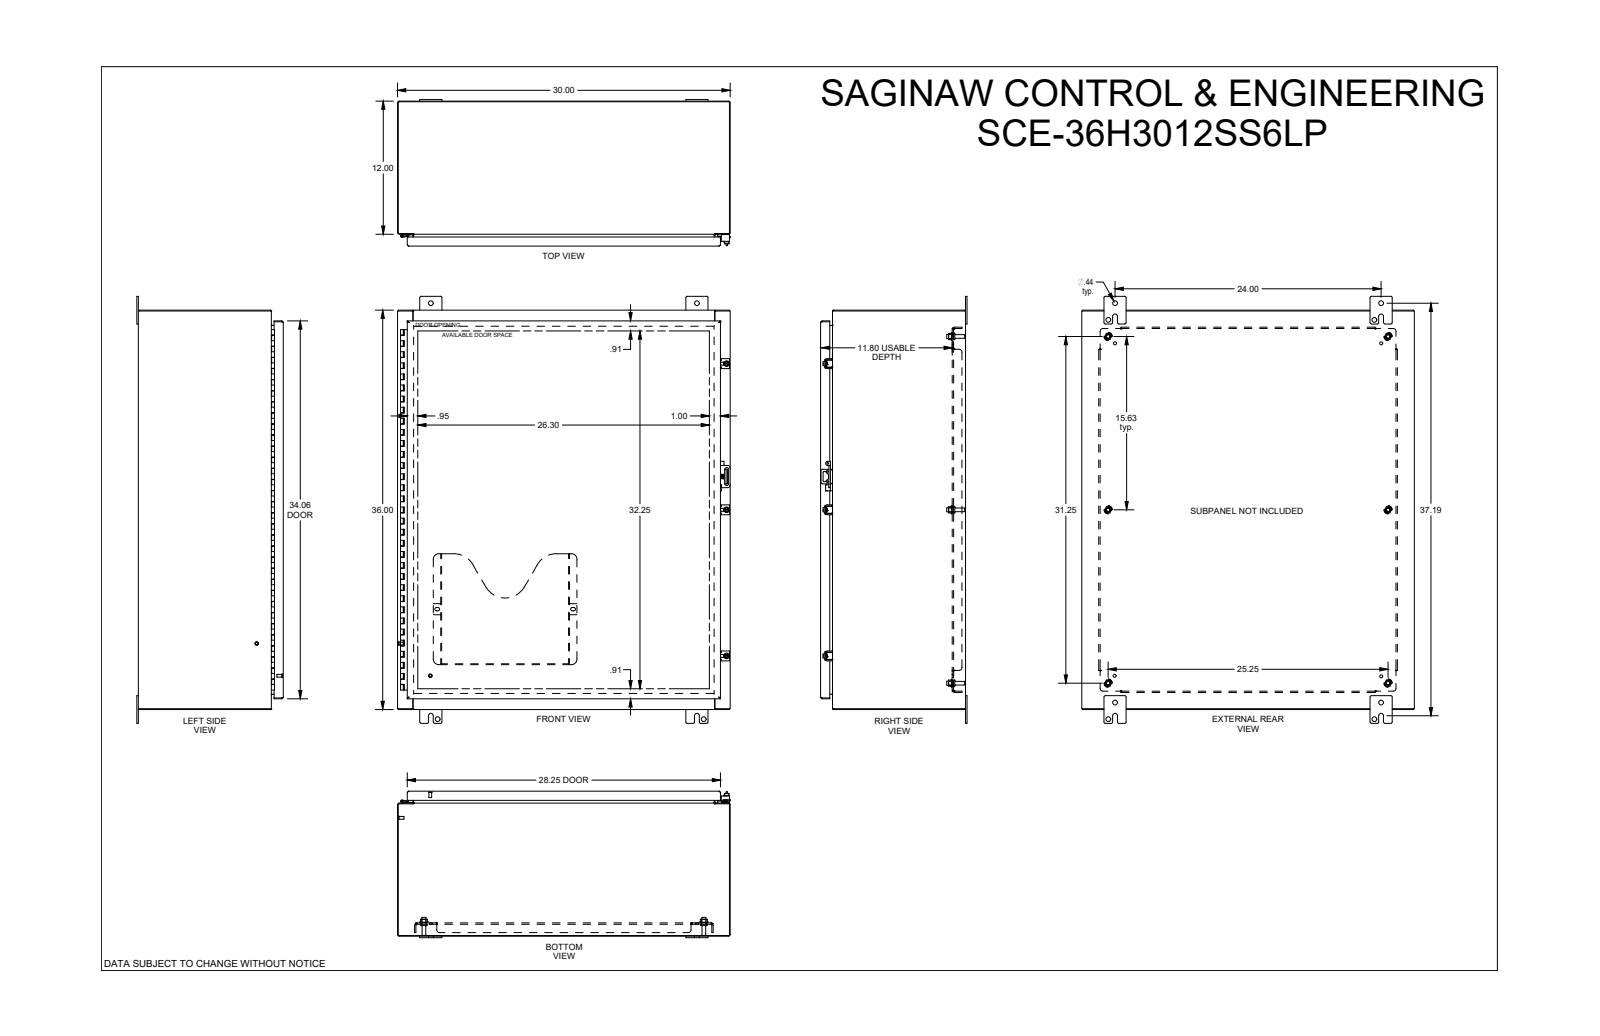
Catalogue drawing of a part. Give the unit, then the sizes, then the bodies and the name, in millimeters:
Units: millimetres
Overall size (bounding box): 977.9 × 762 × 335.5
Round holes (diameter × count): ⌀11.1 ×8, ⌀6.4 ×6, ⌀9.3 ×6, ⌀12.7 ×6, ⌀4.8 ×5, ⌀4.9 ×5, ⌀7.1 ×4, ⌀5.2 ×3, ⌀4.1 ×2, ⌀3.3 ×1, ⌀3.4 ×1
Round bosses / shafts (diameter × count): ⌀6.3 ×8, ⌀14.3 ×6, ⌀9.3 ×6, ⌀8.4 ×6, ⌀6.5 ×5, ⌀4.8 ×5, ⌀6.4 ×4, ⌀12.9 ×3
Partial cylindrical surfaces — rounded edges, fillets, slot ends (radius × count): R0.3 ×160, R0.4 ×40, R0.7 ×36, R1.5 ×29, R0.8 ×27, R3.2 ×27, R1 ×22, R1.8 ×14
Main face-to-face distances: 1.9, 1.9, 330.1, 328.2, 30.5, 301.6, 332.1, 330.1, 302.8, 28.6
Hole centre spacings: 41.1, 609.6, 914.4, 1099, 13.1, 200, 200, 381.5
Bodies: 0 solids, 4019 faces (1647 planar, 844 cylindrical, 1528 other)
Part name (STEP PRODUCT): SCE-36H3012SS6LP
STEP written by: SolidWorks 2019 (CONFIG_CONTROL_DESIGN)
